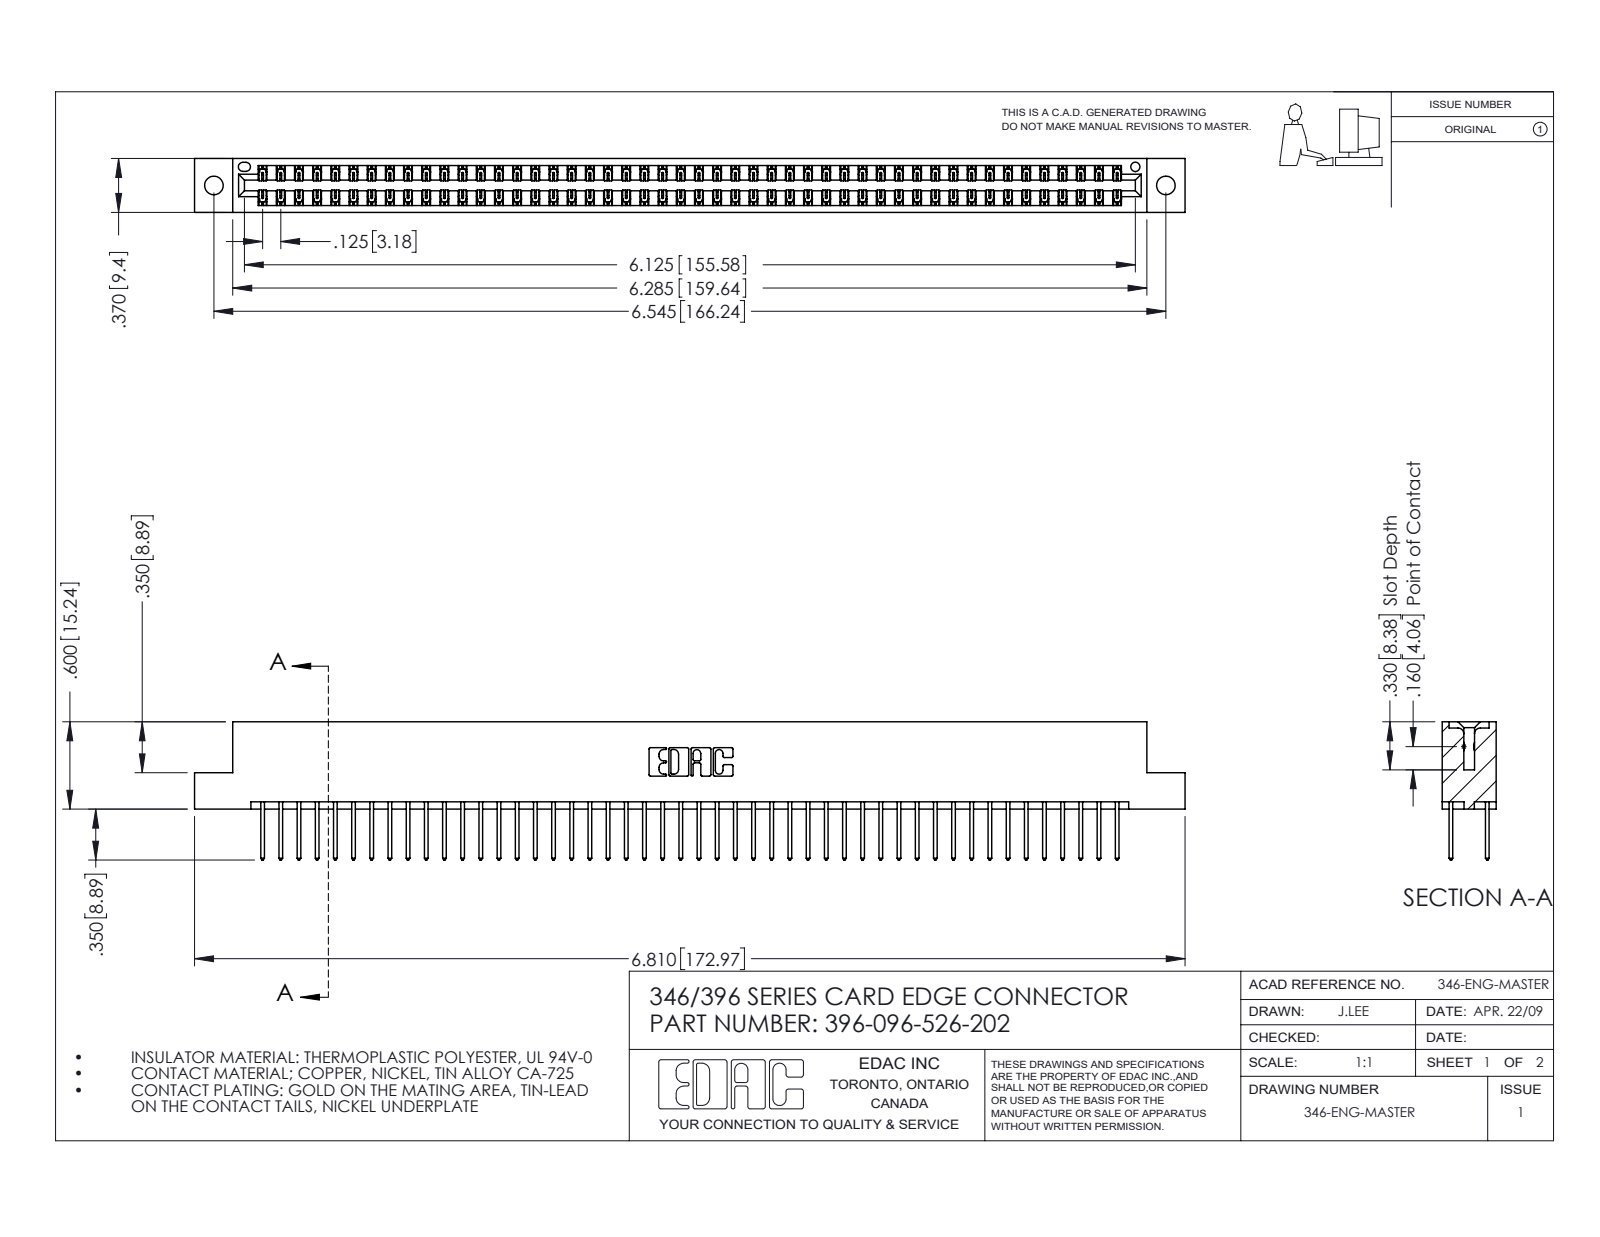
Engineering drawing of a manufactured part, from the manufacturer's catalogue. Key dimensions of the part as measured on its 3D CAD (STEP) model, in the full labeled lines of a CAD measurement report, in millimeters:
Part name (STEP PRODUCT): 396-096-526-202; 345-292-001_345-293-126; 346 Part_Flush Mounting Lugs - 0.128 Dia
STEP written by: SolidWorks 2016 (CONFIG_CONTROL_DESIGN)
Units: millimetres
Bodies: 97 solids, 5114 faces (3436 planar, 1678 cylindrical, 0 other)
Overall size (bounding box): 173 × 24.1 × 9.4
Volume: 17 040 mm³ · Surface area: 23 940 mm²
Round holes (diameter × count): ⌀3.3 ×2, ⌀1.6 ×1
Partial cylindrical surfaces — rounded edges, fillets, slot ends (radius × count): R0.2 ×144, R0.3 ×96, R0.3 ×22, R0.2 ×6, R0.8 ×6, R0.7 ×3, R0.4 ×2, R0.6 ×2
Main face-to-face distances: 1.2, 8.2, 6.4, 9.4, 1.8, 7.6, 0.6, 7, 3.8, 5.6
Hole centre spacings: 6.2, 160.9, 166.2
